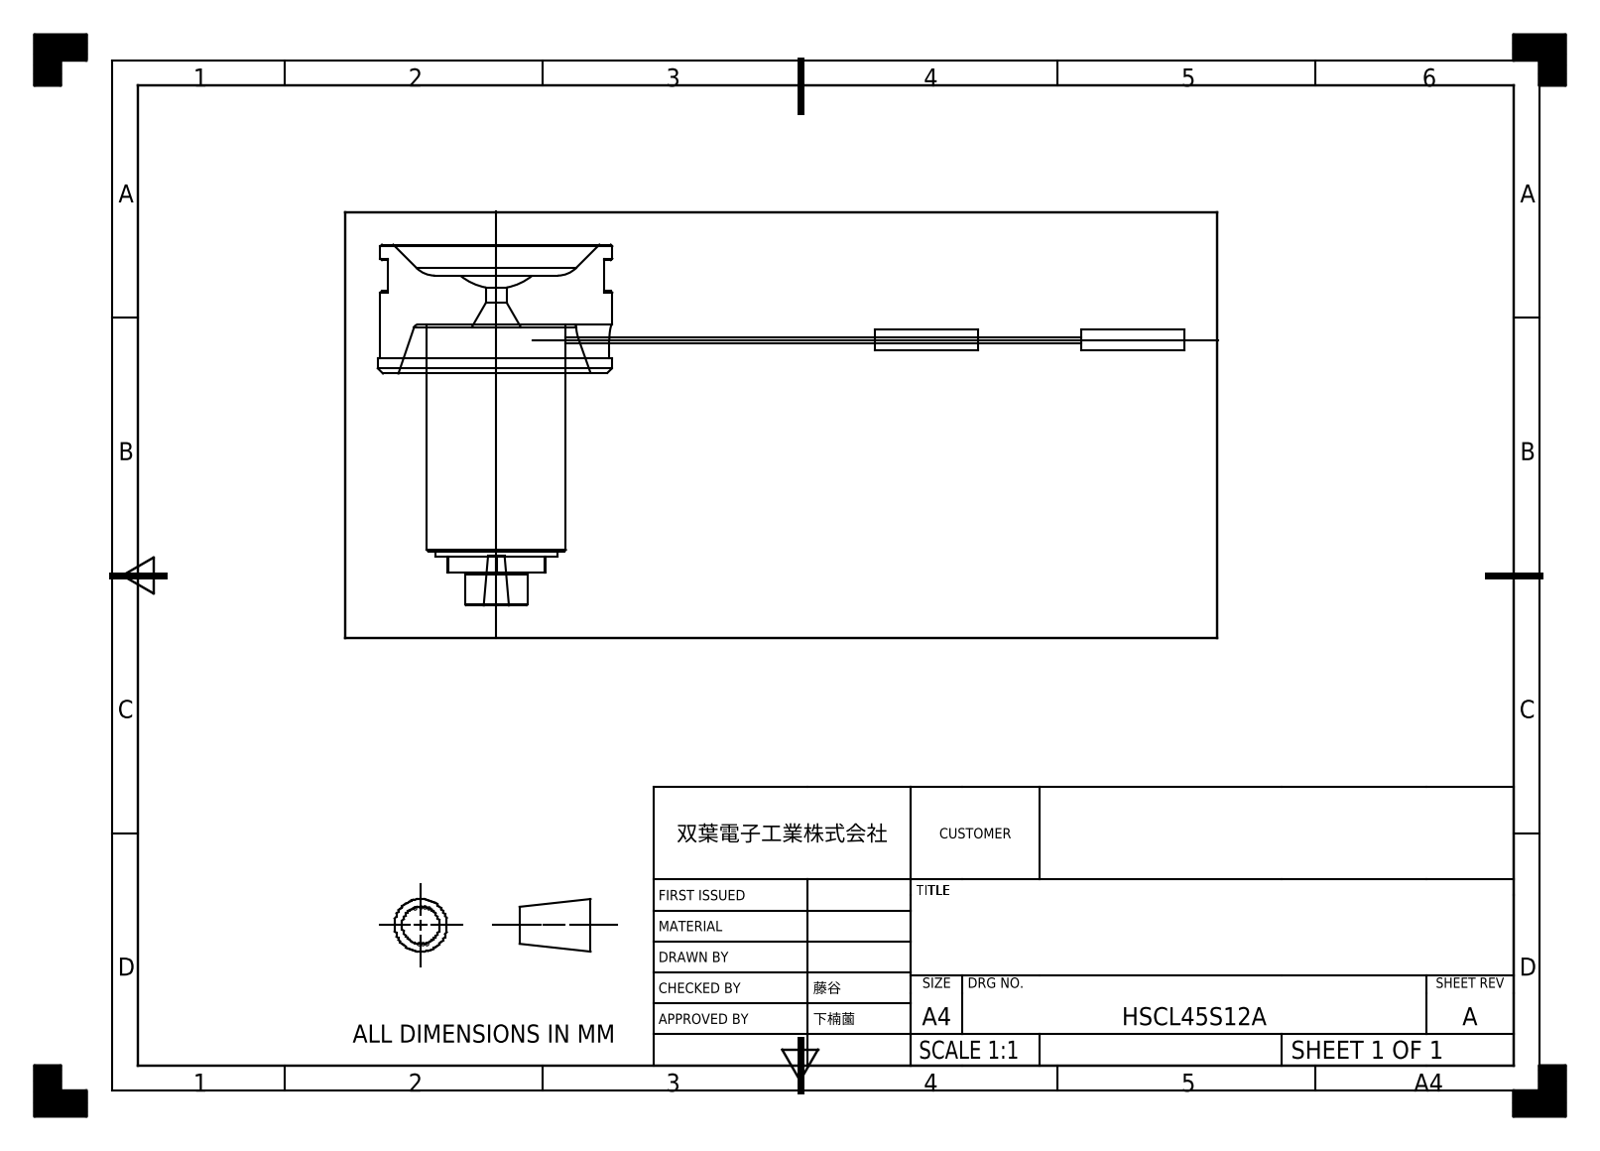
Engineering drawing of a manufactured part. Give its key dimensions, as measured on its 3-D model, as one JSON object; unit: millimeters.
{"part_name": "HSCL45S12A", "step_written_by": "SIEMENS PLM Software NX 2023 (AUTOMOTIVE_DESIGN)", "units": "millimeters", "bodies": {"solids": 3, "faces": 65, "planar": 31, "cylindrical": 18, "other": 16}, "overall_size": [156.5, 70, 46], "volume_mm3": 52214, "surface_area_mm2": 13437, "round_holes": [[4, 1]], "round_bosses_or_shafts": [[4, 2], [1.2, 2], [46, 1], [45, 1], [27, 1], [23.8, 1], [12, 1]], "partial_cylinders_radius": [[3, 2], [10.9, 1]], "face_to_face_distances": [9.5, 19, 6, 25, 54.5, 45, 63.7, 57.7, 38.7, 15.5]}
